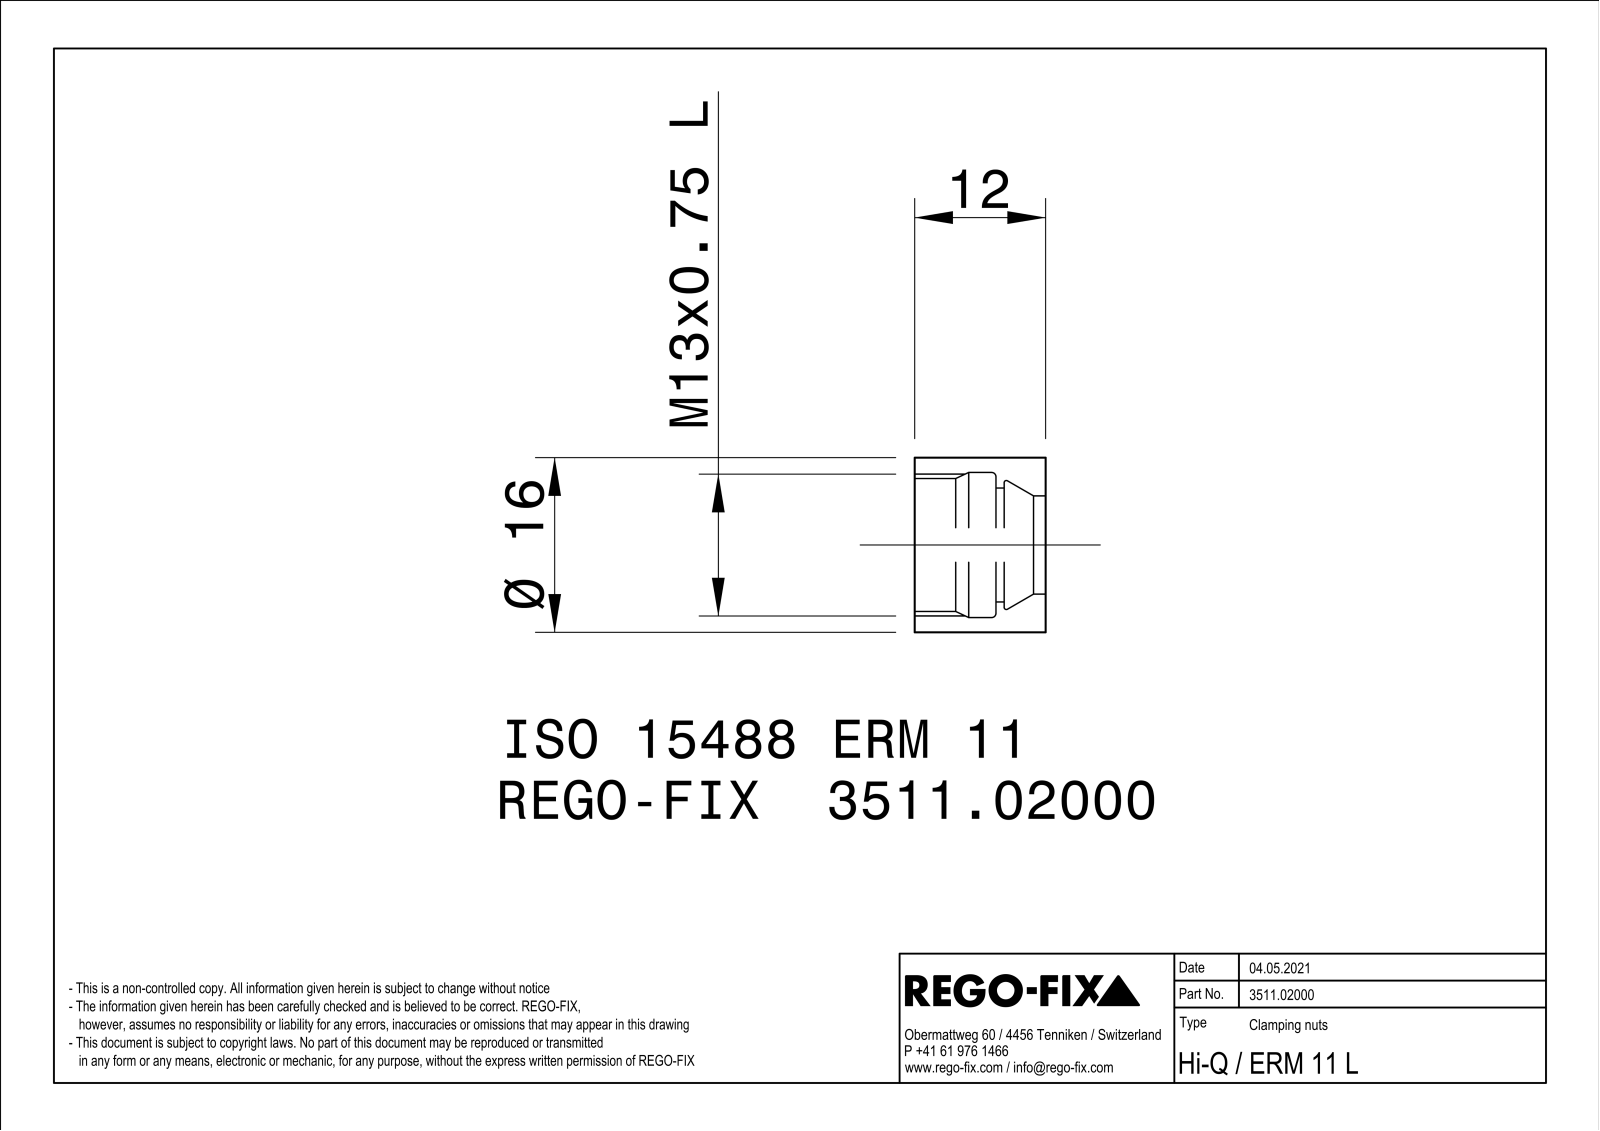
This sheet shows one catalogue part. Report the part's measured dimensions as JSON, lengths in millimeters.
{"part_name": "NOCUT", "step_written_by": "SIEMENS PLM Software Solid Edge ST10 (AUTOMOTIVE_DESIGN)", "units": "millimeters", "bodies": {"solids": 1, "faces": 38, "planar": 22, "cylindrical": 5, "other": 11}, "overall_size": [16, 16, 12], "volume_mm3": 1001, "surface_area_mm2": 1351, "round_holes": [[9, 1], [10.44, 1], [12.19, 1], [13.3, 1]], "round_bosses_or_shafts": [[16, 1]], "face_to_face_distances": [12, 4.55, 7.45, 3, 3.8, 0.75, 8.2]}
